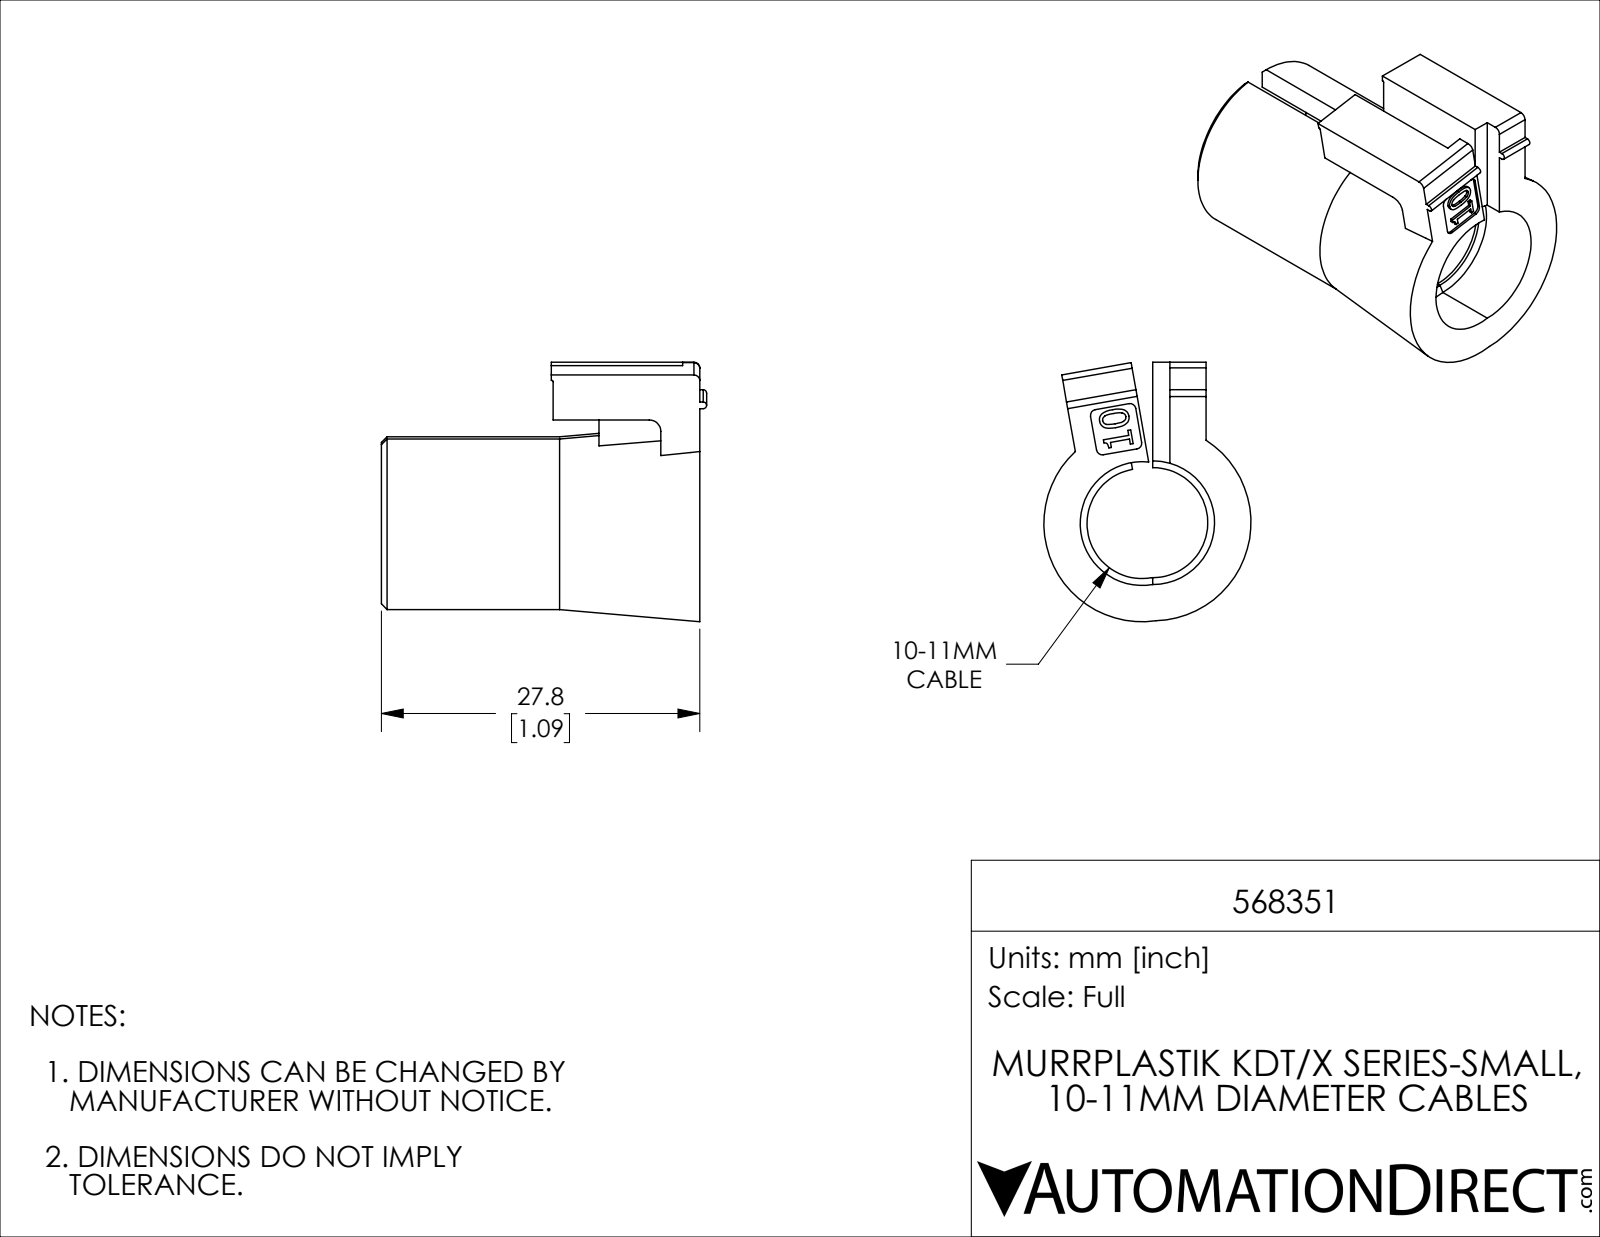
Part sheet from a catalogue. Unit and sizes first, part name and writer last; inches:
Units: inches
Overall size (bounding box): 1.118 × 0.892 × 0.712
Partial cylindrical surfaces — rounded edges, fillets, slot ends (radius × count): R0.02 ×6, R0.004 ×2, R0.012 ×2, R0.039 ×2, R0.189 ×2, R0.213 ×2, R0.295 ×2
Main face-to-face distances: 0.183, 1.094, 0.157, 0.059, 0.504, 0.591, 0.445, 1.035, 0.158, 0.346
Volume: 0.201 in³ · Surface area: 4.953 in²
Bodies: 1 solid, 102 faces (51 planar, 26 cylindrical, 25 other)
Part name (STEP PRODUCT): 568351
STEP written by: SolidWorks 2019 (CONFIG_CONTROL_DESIGN)
